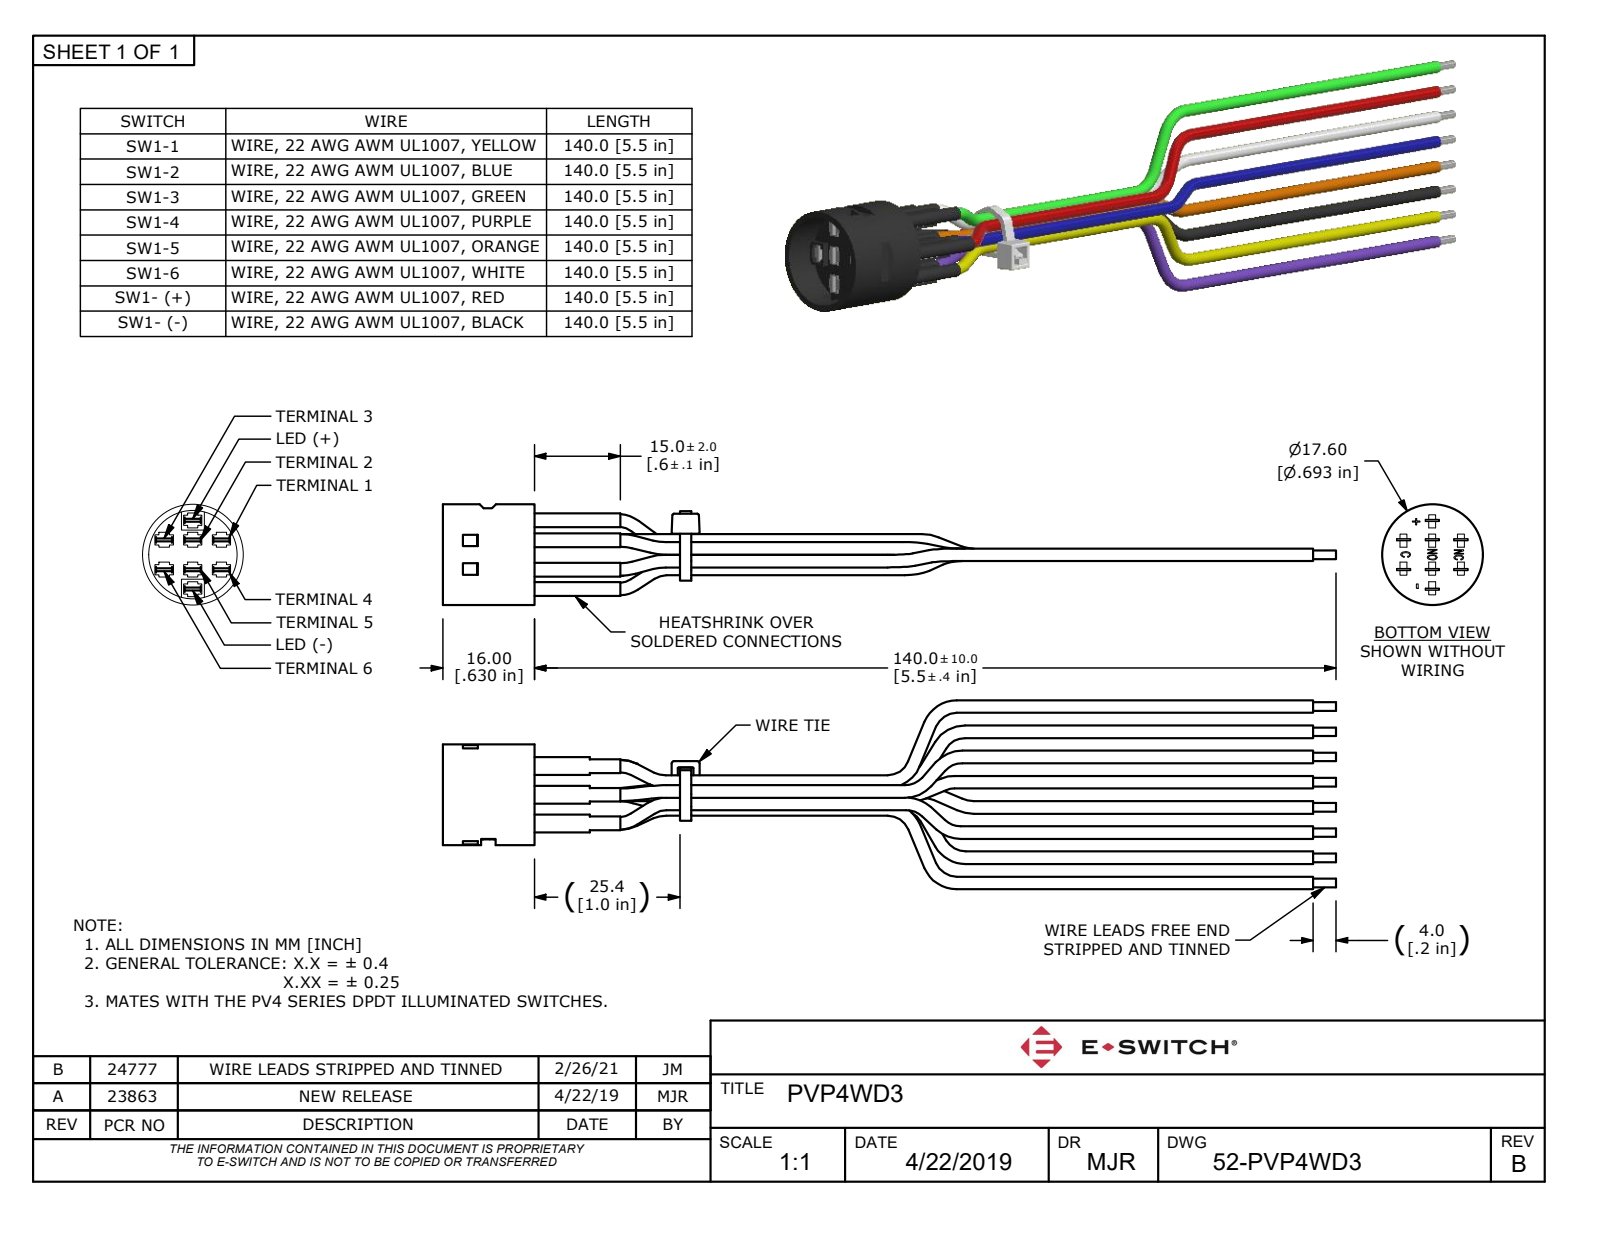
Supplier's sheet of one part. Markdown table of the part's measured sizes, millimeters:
| quantity | value |
| --- | --- |
| part name | PVP4WD3 |
| STEP written by | Autodesk Inventor 2018 (AP242_MANAGED_MODEL_BASED_3D_ENGINEERING_MIM_LF) |
| units | millimeters |
| bodies | 1 solid, 814 faces (600 planar, 107 cylindrical, 107 other) |
| overall size | 156 × 33 × 17.6 |
| volume | 7 118 mm³ |
| surface area | 10 867 mm² |
| round holes (diameter × count) | 15.4 × 1 |
| round bosses / shafts (diameter × count) | 2.2 × 33, 2.4 × 8, 1.5 × 8, 17.6 × 1 |
| partial cylindrical surfaces (radius × count) | 0.25 × 16, 0.2 × 14, 1.1 × 11, 2 × 5 |
| main face-to-face distances | 5.2, 0.5, 9.9, 0.65, 5.7, 3.4, 8.6, 2, 5, 7.95 |
